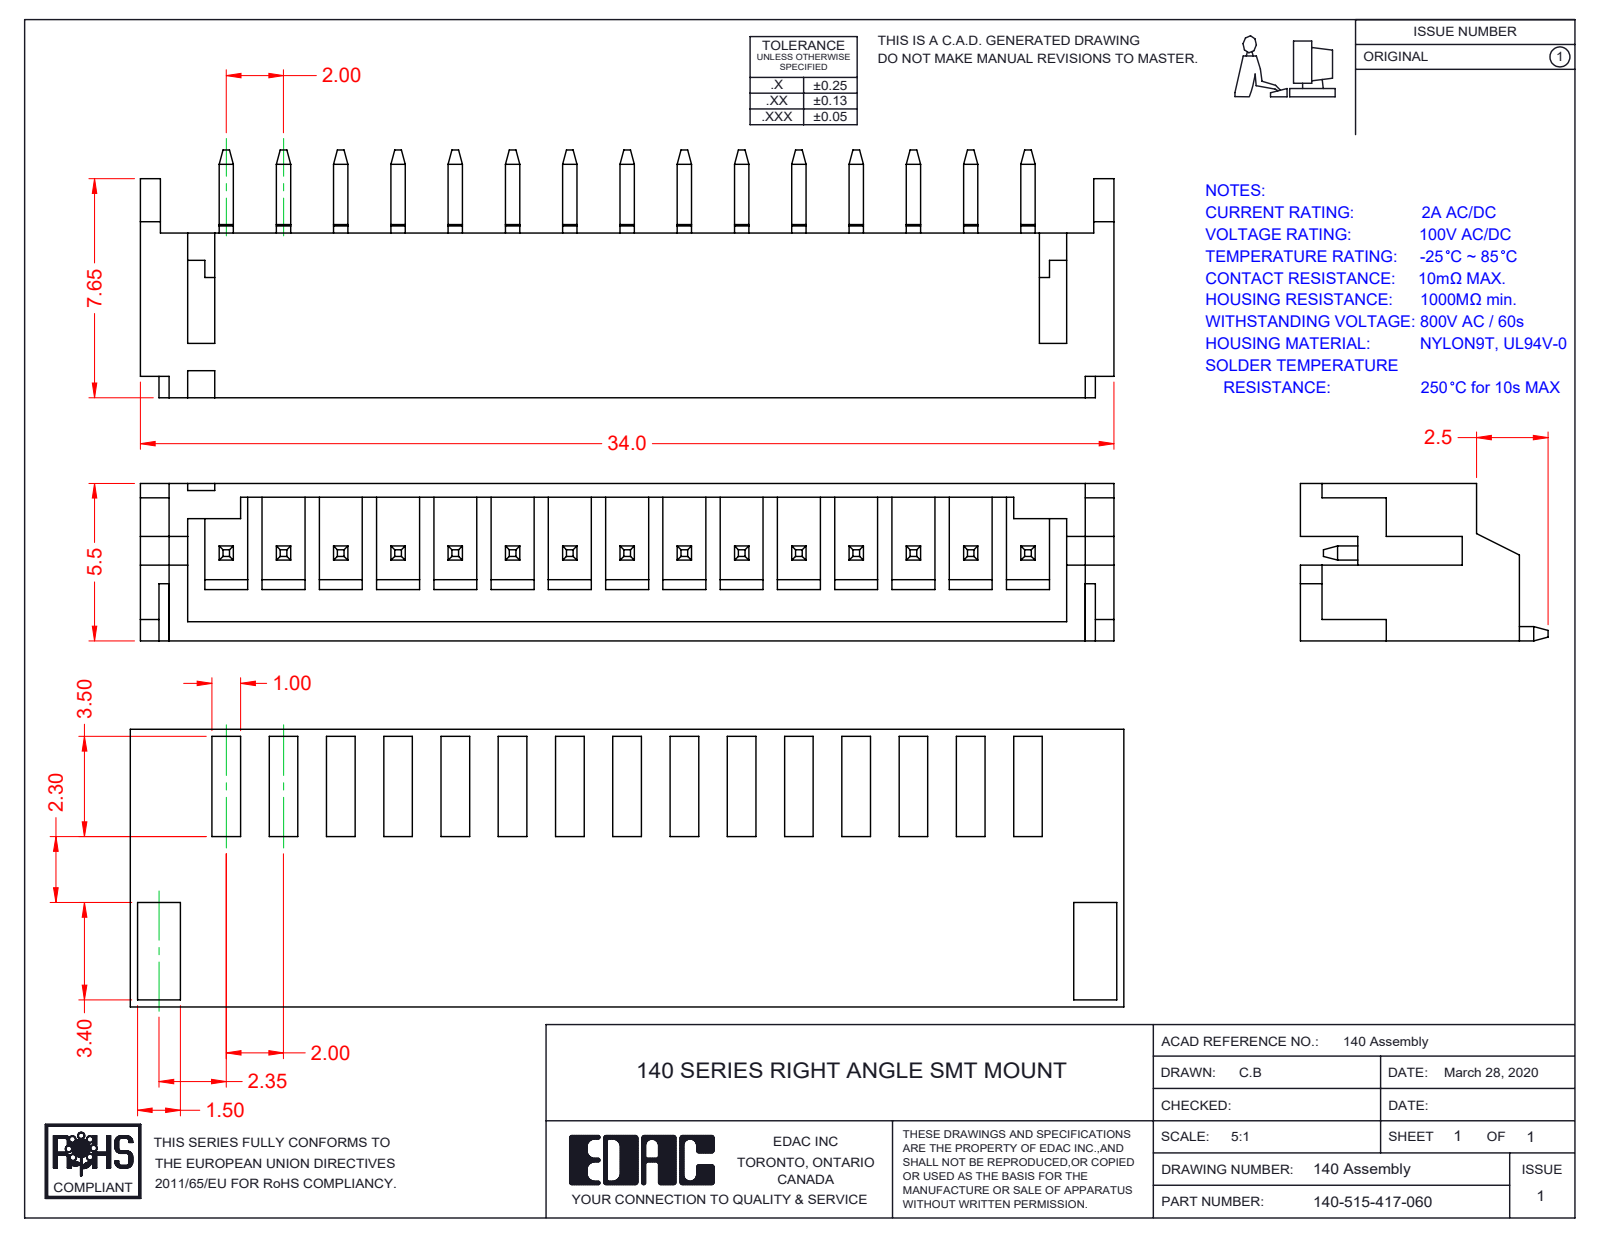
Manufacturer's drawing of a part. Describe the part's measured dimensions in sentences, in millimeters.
The part is named "RA SMT Pad; 140-515-417-060; RA SMT Contact; RA SMT Housing_515". Its 3-D file was written by "SolidWorks 2016 (CONFIG_CONTROL_DESIGN)". It is 18 solids with 770 faces: 710 planar, 60 cylindrical and 0 other. Overall it measures 34 by 8.65 by 5.5 millimeters. Its volume is 444 cubic millimeters and its surface area 1 701 square millimeters. Partial cylindrical surfaces (rounded edges, fillets, slot ends): 2 of radius 0.55. The main face-to-face distances are 5.5, 0.67, 0.65, 4.83, 4.35, 5.02, 0.48, 0.5, 0.95, 0.9.
